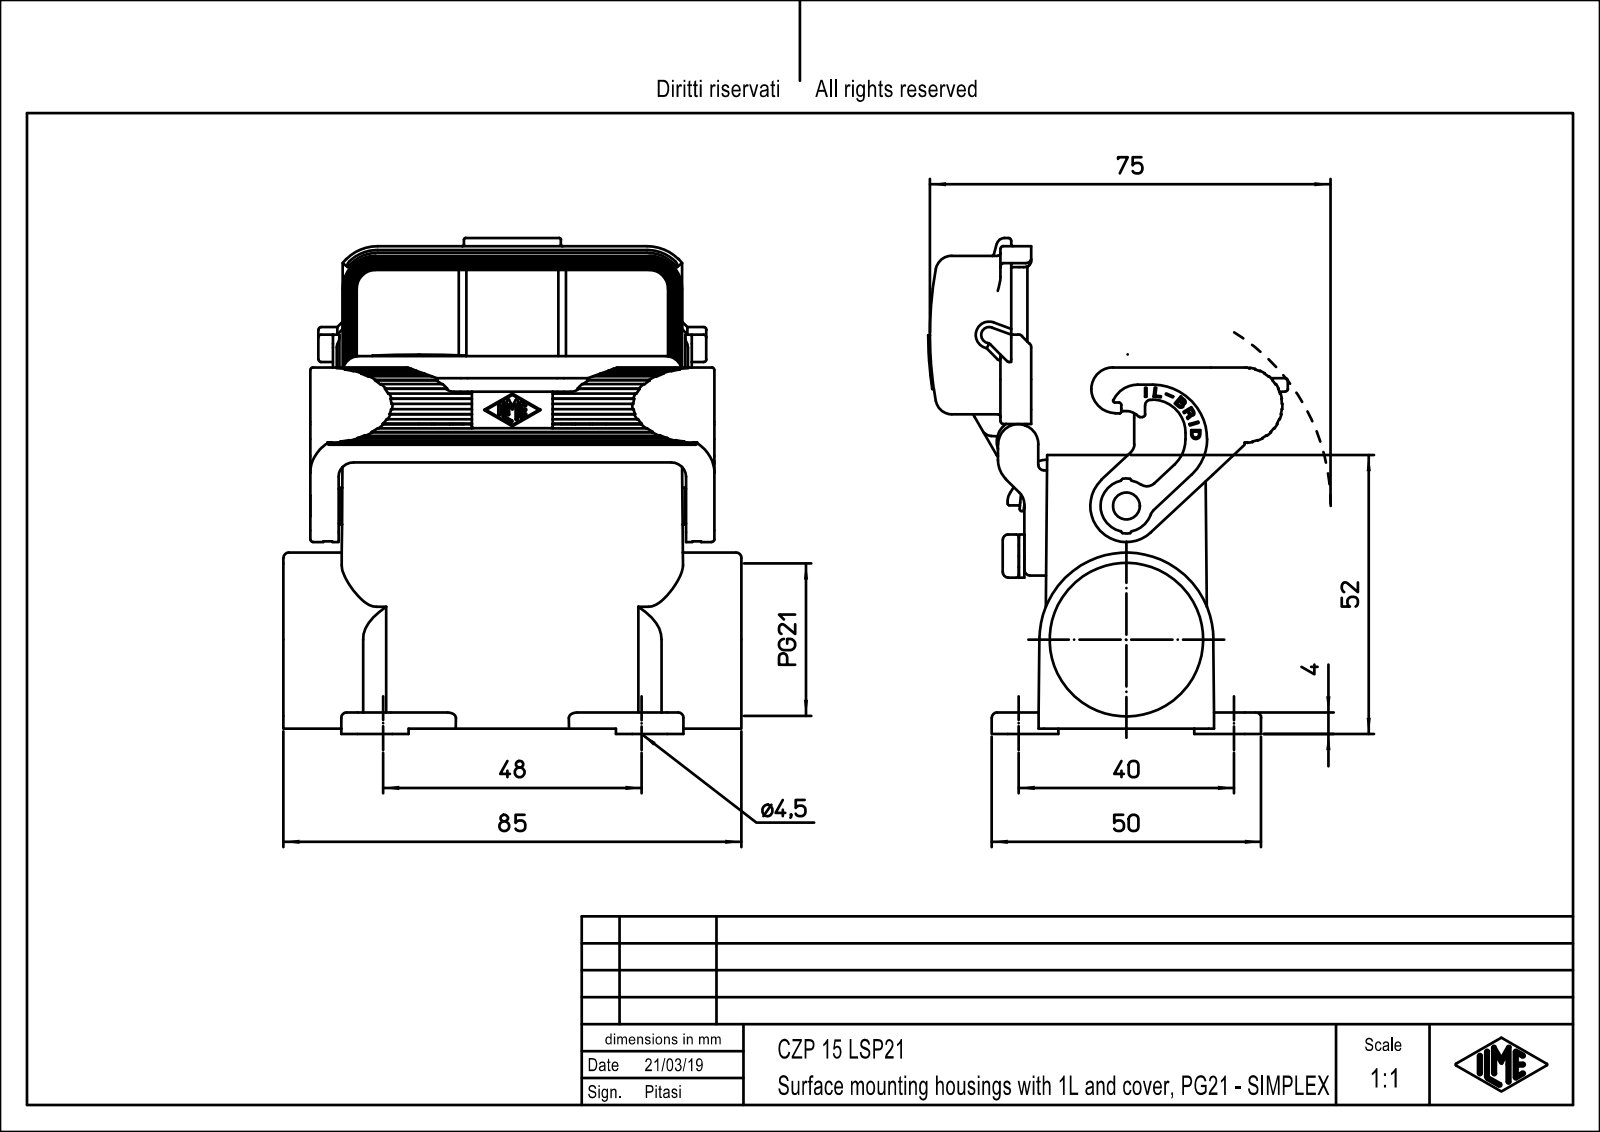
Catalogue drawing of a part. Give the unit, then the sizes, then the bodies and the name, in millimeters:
Units: millimetres
Overall size (bounding box): 92.85 × 85 × 66.66
Round holes (diameter × count): ⌀3 ×4, ⌀4.5 ×4, ⌀5 ×1, ⌀23 ×1, ⌀28.3 ×1
Round bosses / shafts (diameter × count): ⌀8.4 ×1, ⌀8 ×1, ⌀6.8 ×1, ⌀4.8 ×1, ⌀2.4 ×1
Partial cylindrical surfaces — rounded edges, fillets, slot ends (radius × count): R3 ×13, R6.5 ×7, R2 ×4, R3.4 ×4, R3.5 ×4, R3.5 ×4, R6.3 ×4, R4 ×3
Main face-to-face distances: 2.6, 26.8, 24.2, 3, 29.4, 26.81, 3.8, 6.4, 30.6, 33.2
Hole centre spacings: 12.02, 28.01, 50.21, 56.22, 16, 40, 48, 49.5
Volume: 70 509 mm³ · Surface area: 47 242 mm²
Bodies: 1 solid, 495 faces (289 planar, 186 cylindrical, 20 other)
Part name (STEP PRODUCT): CZP_15_LSP21
STEP written by: PTC Creo Elements/Direct Modeling 19.0E 27-Jun-2016 (C) Parametric Technology GmbH (AUTOMOTIVE_DESIGN)
